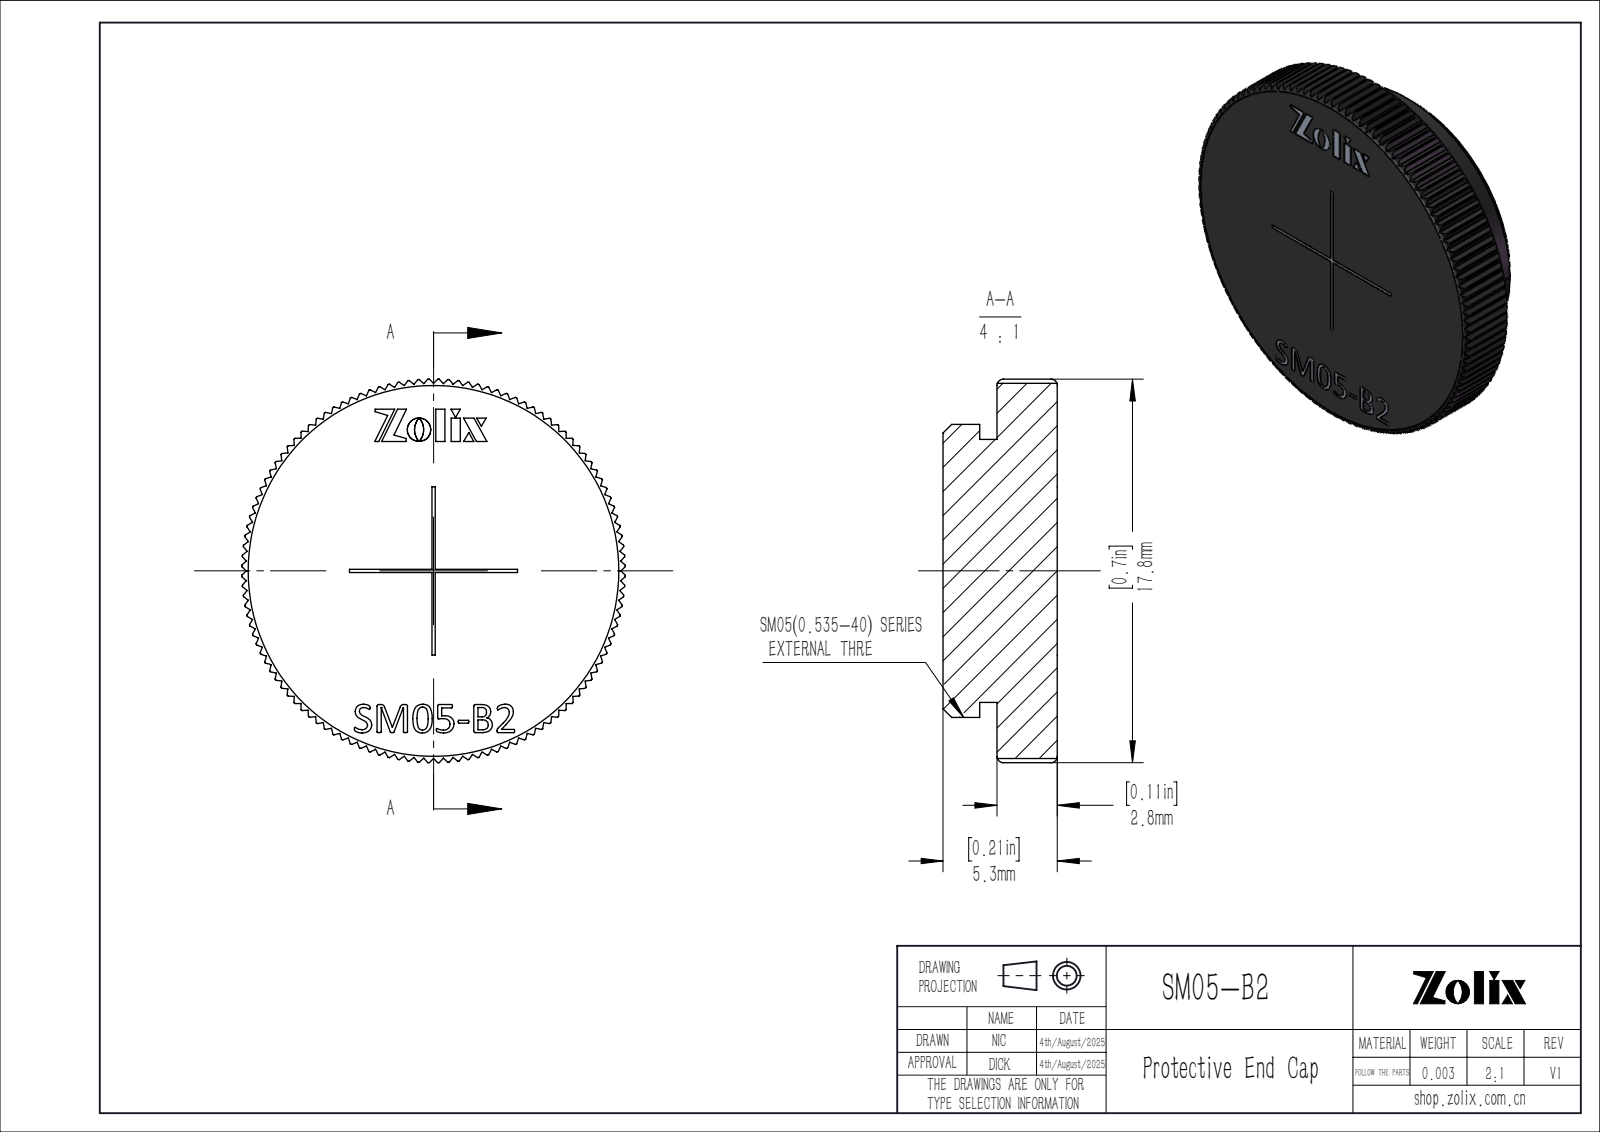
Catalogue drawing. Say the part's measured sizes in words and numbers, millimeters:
The part is named "SM05-B2". Its 3-D file was written by "SolidWorks 2020 (CONFIG_CONTROL_DESIGN)". It is 1 solid with 658 faces: 460 planar, 124 cylindrical and 74 other. Overall it measures 17.8 by 17.8 by 5.3 millimeters. Its volume is 1 019 cubic millimeters and its surface area 839 square millimeters. Round bosses or shafts: 1 of diameter 13.59, 1 of diameter 12.2. Partial cylindrical surfaces (rounded edges, fillets, slot ends): 1 of radius 8.9. The main face-to-face distances are 5.3, 2.8, 2.5, 12.3, 3.6, 0.8, 1.7, 12.31, 2.78, 3.58.
